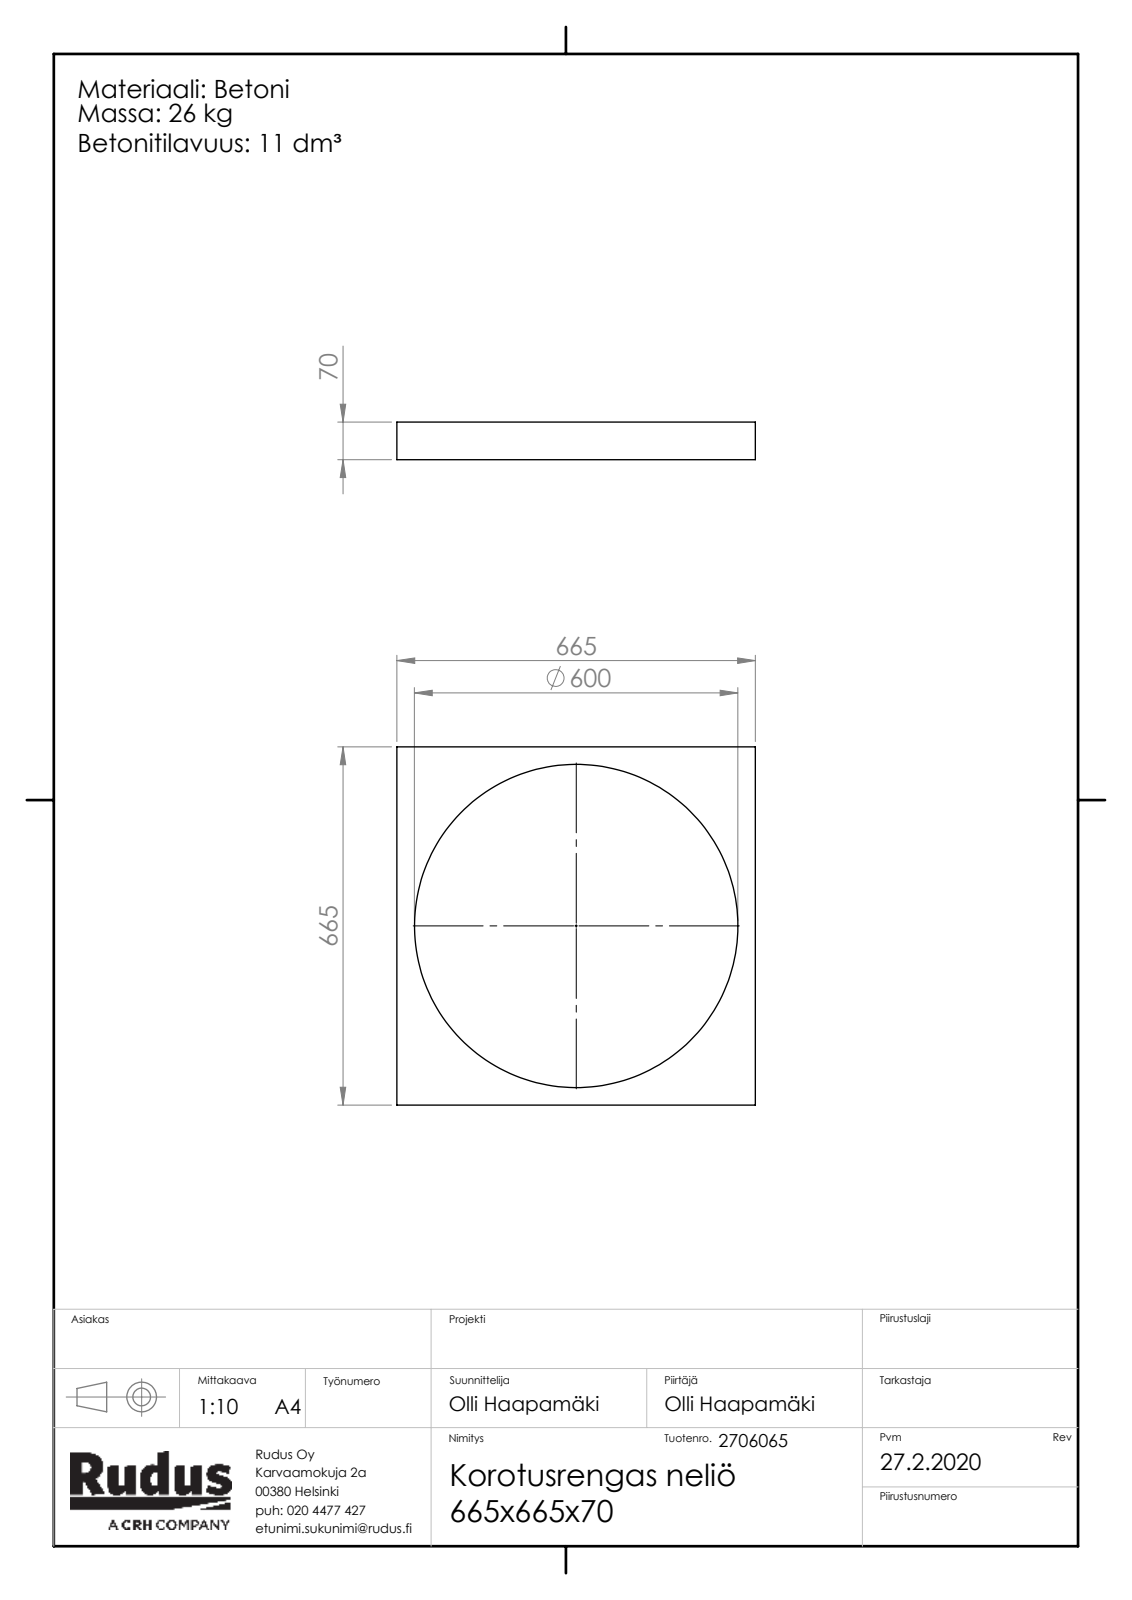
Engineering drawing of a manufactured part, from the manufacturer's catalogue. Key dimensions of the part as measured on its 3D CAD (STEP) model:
Part name (STEP PRODUCT): kaivo-osa-korotusrengas-nelio_nelikorkkari; Rudus 2706065 Korotusrengas neliö 665x665x70
STEP written by: SolidWorks 2019 (CONFIG_CONTROL_DESIGN)
Units: millimetres
Bodies: 1 solid, 77 faces (44 planar, 2 cylindrical, 31 other)
Overall size (bounding box): 665 × 665 × 70
Volume: 11 160 000 mm³ · Surface area: 639 201 mm²
Round holes (diameter × count): ⌀600 ×1
Main face-to-face distances: 70, 665, 3, 662, 5.38, 55.77, 14.23, 50.77, 300.19, 364.81
